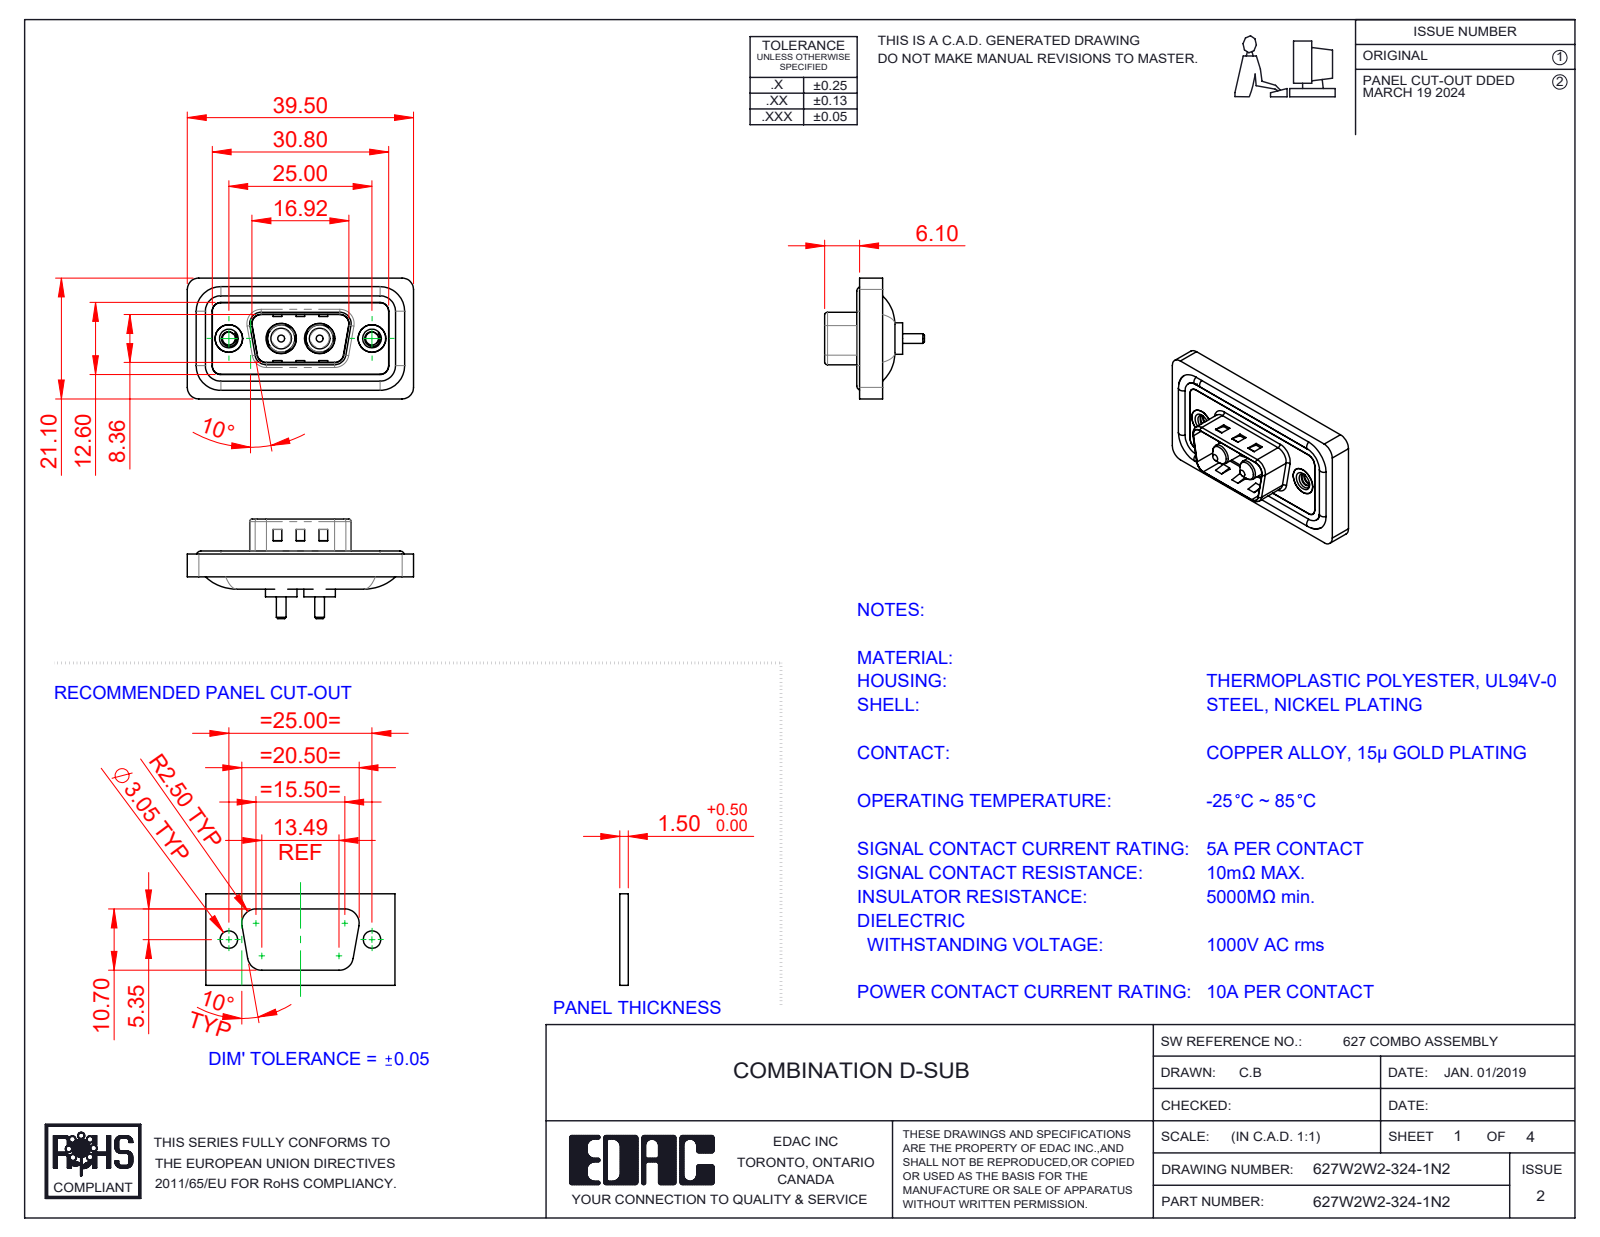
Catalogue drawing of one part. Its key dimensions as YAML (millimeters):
part_name: "Power Pin_10A S; 627Combo Shell Front_09 Contacts; 627Combo Housing_2W2; 627Combo Waterproof Housing_09 Contacts (+3 more)"
step_written_by: "SolidWorks 2023 (CONFIG_CONTROL_DESIGN)"
units: millimeters
bodies: {solids: 11, faces: 489, planar: 165, cylindrical: 218, other: 106}
overall_size: [39.5, 21.1, 17.4]
volume: 4431
surface_area: 6959
round_holes:
  - {diameter: 2.26, count: 2}
  - {diameter: 4, count: 2}
  - {diameter: 4.8, count: 2}
  - {diameter: 4.85, count: 2}
  - {diameter: 5, count: 2}
  - {diameter: 5.3, count: 2}
round_bosses_or_shafts:
  - {diameter: 1.6, count: 4}
  - {diameter: 5.5, count: 2}
  - {diameter: 5.2, count: 2}
  - {diameter: 4.9, count: 2}
  - {diameter: 4.75, count: 2}
  - {diameter: 3.75, count: 2}
  - {diameter: 3.6, count: 2}
  - {diameter: 1.7, count: 2}
partial_cylinders:
  - {radius: 1.5, count: 22}
  - {radius: 2, count: 18}
  - {radius: 0.5, count: 8}
  - {radius: 1.6, count: 8}
  - {radius: 0.25, count: 4}
  - {radius: 0.6, count: 4}
  - {radius: 0.65, count: 4}
  - {radius: 0.9, count: 4}
face_to_face_distances: [0.4, 1.1, 2.9, 3.1, 0.5, 1.5, 1.6, 4, 2.5, 0.7]
hole_center_spacings: [9.14, 15.86, 6.72, 25]
